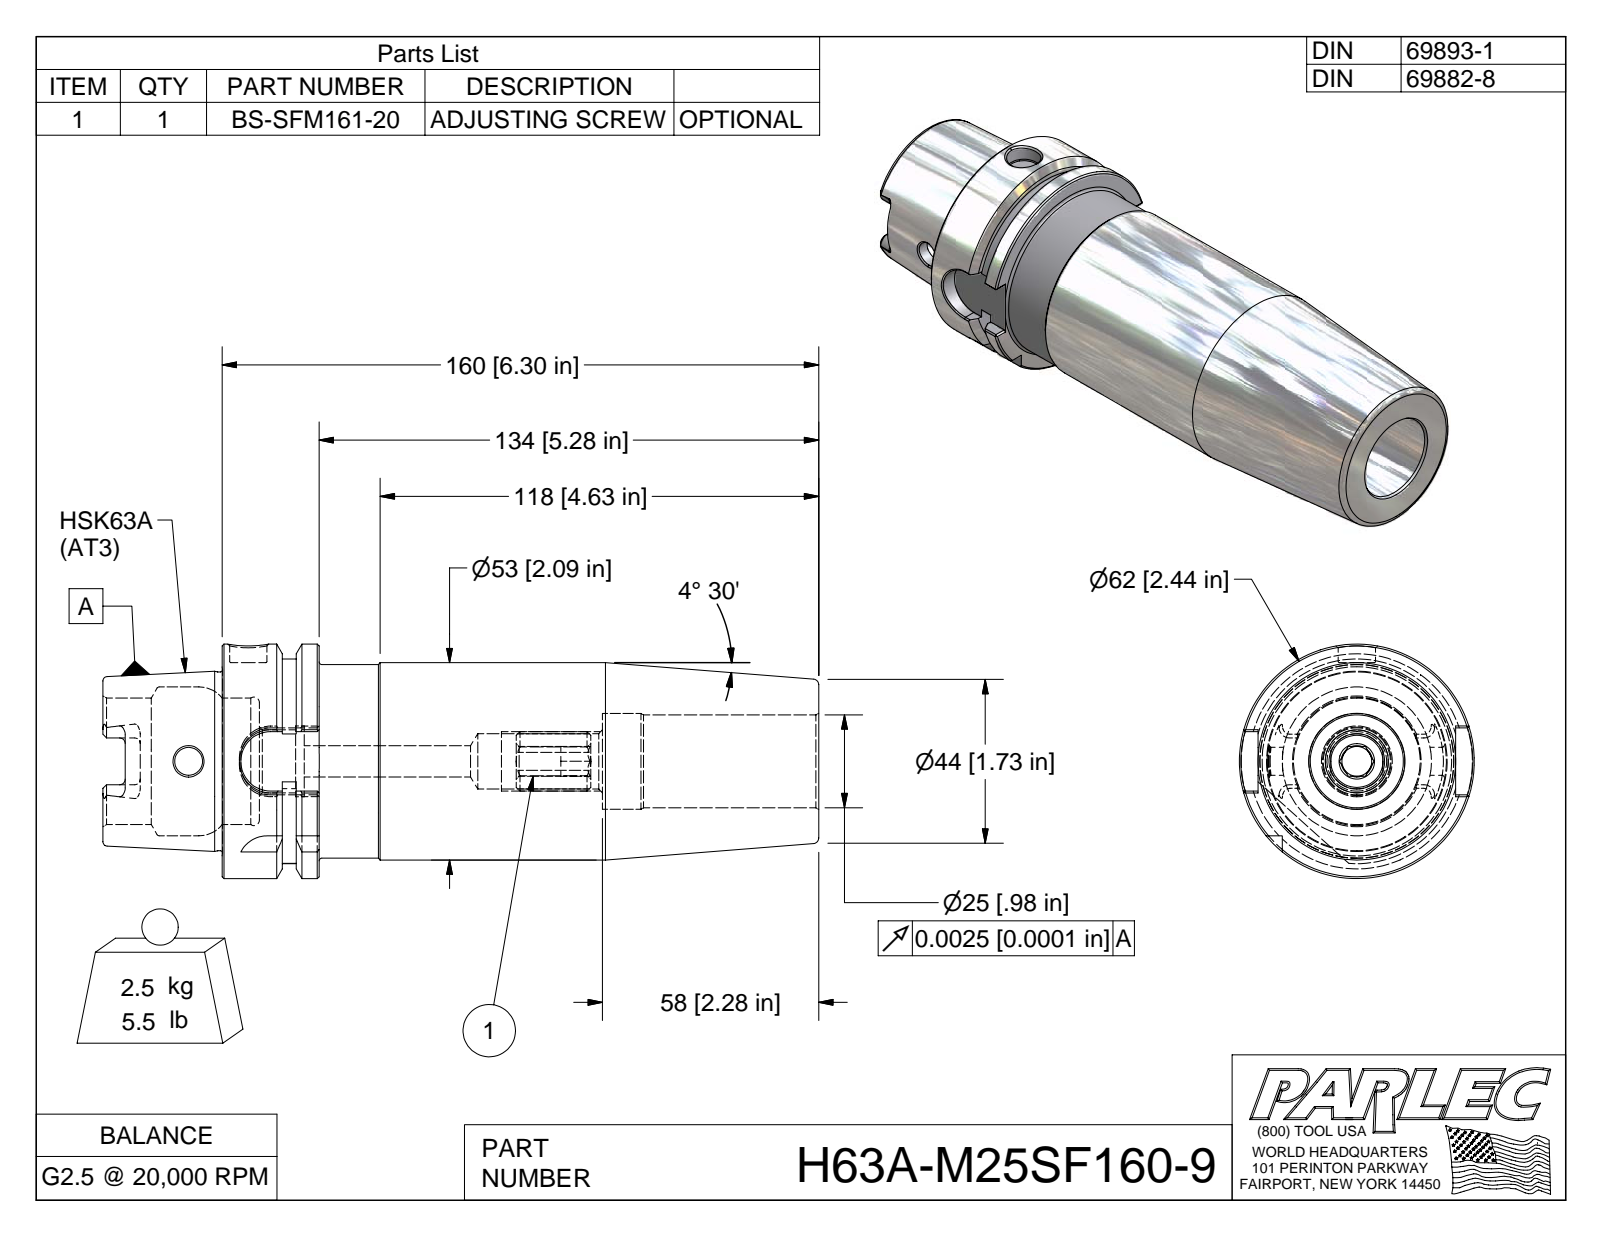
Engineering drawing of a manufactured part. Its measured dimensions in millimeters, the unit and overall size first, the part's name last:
Units: millimetres
Overall size (bounding box): 192 × 63 × 63
Round holes (diameter × count): ⌀7.5 ×1, ⌀10 ×1, ⌀16.9 ×1, ⌀19 ×1, ⌀25 ×1, ⌀25.7 ×1, ⌀34 ×1, ⌀40 ×1
Round bosses / shafts (diameter × count): ⌀63 ×1, ⌀53 ×1, ⌀52 ×1, ⌀48 ×1
Partial cylindrical surfaces — rounded edges, fillets, slot ends (radius × count): R1.5 ×6, R8 ×5, R2.9 ×4, R27.5 ×1
Main face-to-face distances: 134, 160, 26, 58, 6.1, 9.9, 10, 16, 150, 32
Volume: 320 900 mm³ · Surface area: 52 250 mm²
Bodies: 2 solids, 167 faces (65 planar, 37 cylindrical, 65 other)
Part name (STEP PRODUCT): H63A-M25SF160-9; H63A-M25SF160-9-1; BS-SFM161-20
STEP written by: Autodesk Inventor 2009 (AUTOMOTIVE_DESIGN)
